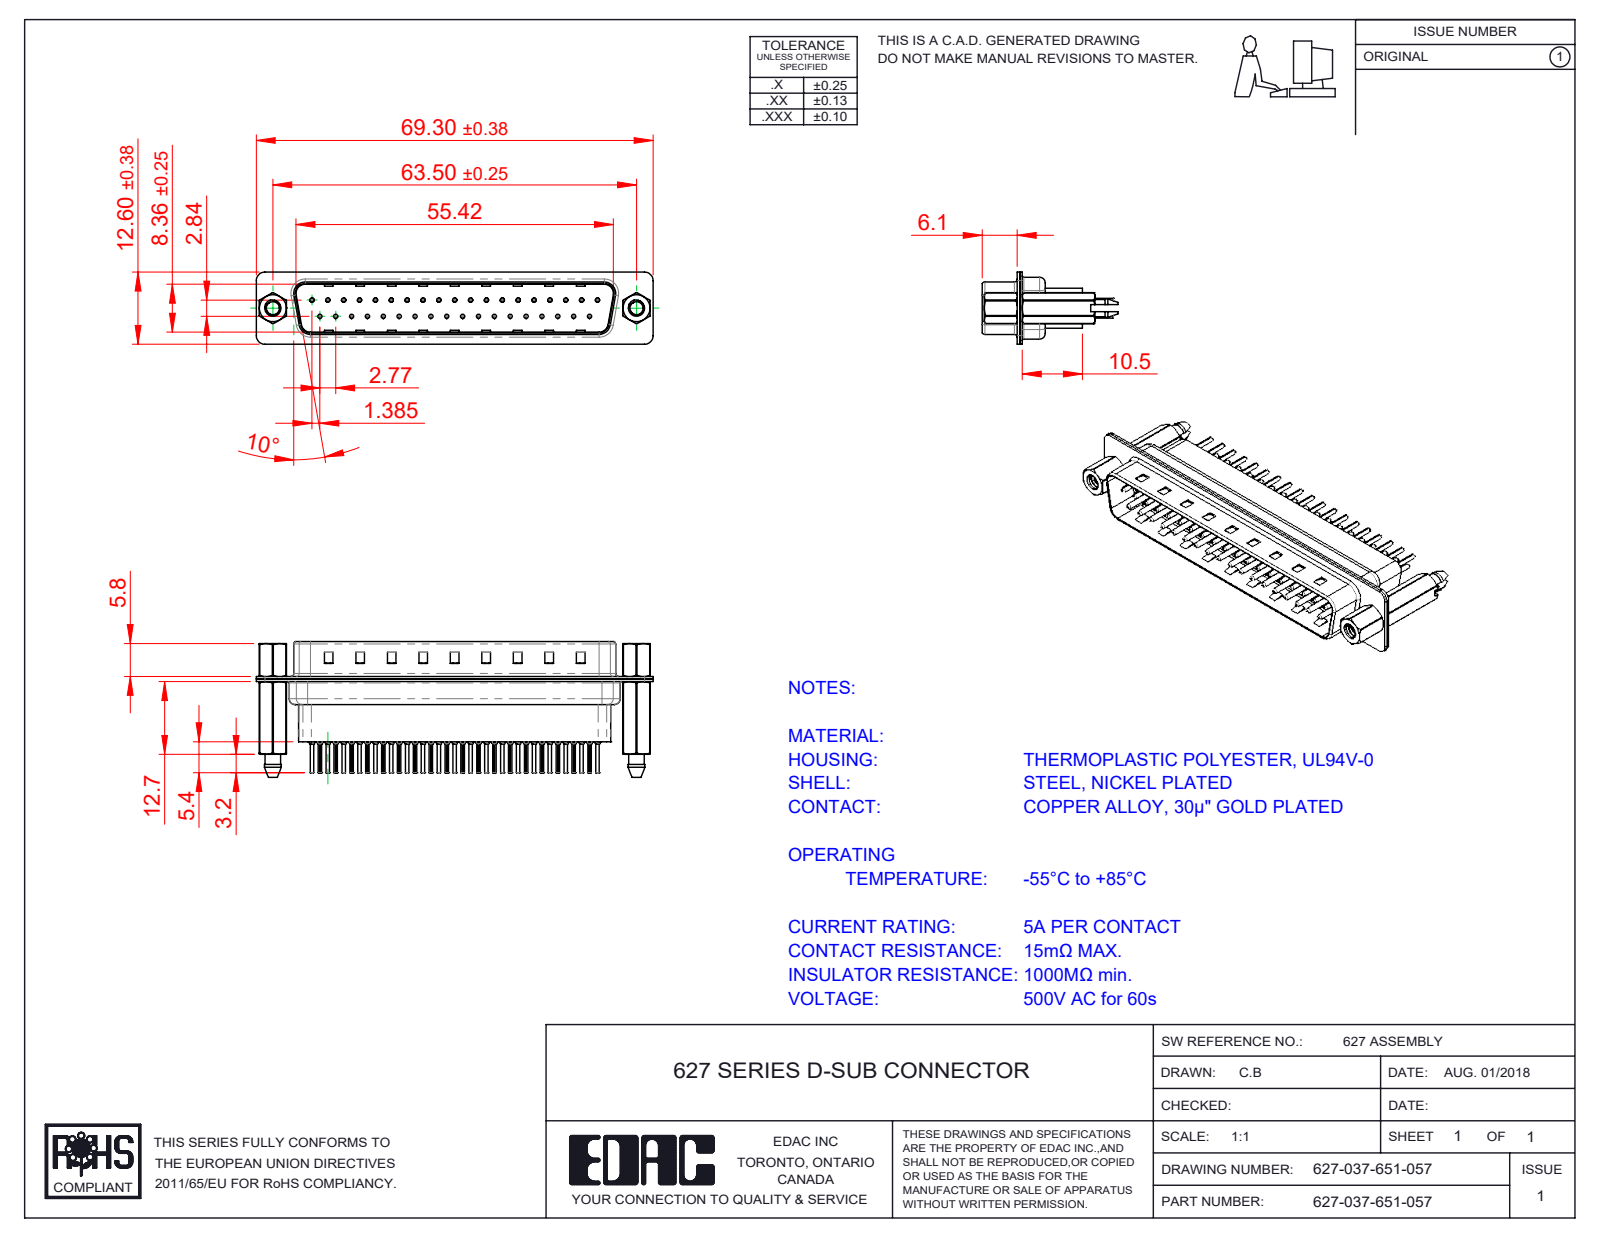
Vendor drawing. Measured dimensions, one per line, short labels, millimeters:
name: 627-037-651-057; 627 Contact Row 2_41; 627 4-40 Threaded Boardlock_HP51; 627 Shell Front_37 Contacts (+4 more)
written by: SolidWorks 2020 (CONFIG_CONTROL_DESIGN)
unit: mm
bodies: 44 solids, 4272 faces (1145 planar, 1648 cylindrical, 1479 other)
size: 69.3 × 23.6 × 12.6
volume: 5 848 mm³; area: 14 927 mm²
holes: 37× ⌀0.2, 37× ⌀0.35, 37× ⌀1.1, 37× ⌀1.6, 2× ⌀2.26, 2× ⌀2.29, 2× ⌀4, 2× ⌀4.8
bosses: 37× ⌀2, 37× ⌀1.5, 37× ⌀0.75, 37× ⌀0.6, 2× ⌀4.9, 2× ⌀2.79
rounds: 74× R0.1, 18× R1.5, 12× R2, 10× R1.6, 8× R0.5, 4× R0.25, 4× R0.6, 4× R0.65
face distances: 0.4, 0.82, 9.58, 0.45, 0.68, 7.68, 1.5, 1.08, 8.08, 8.76
hole spacings: 3.16, 2.77, 5.54, 8.31, 5.04, 10.1, 11.08, 12.78
